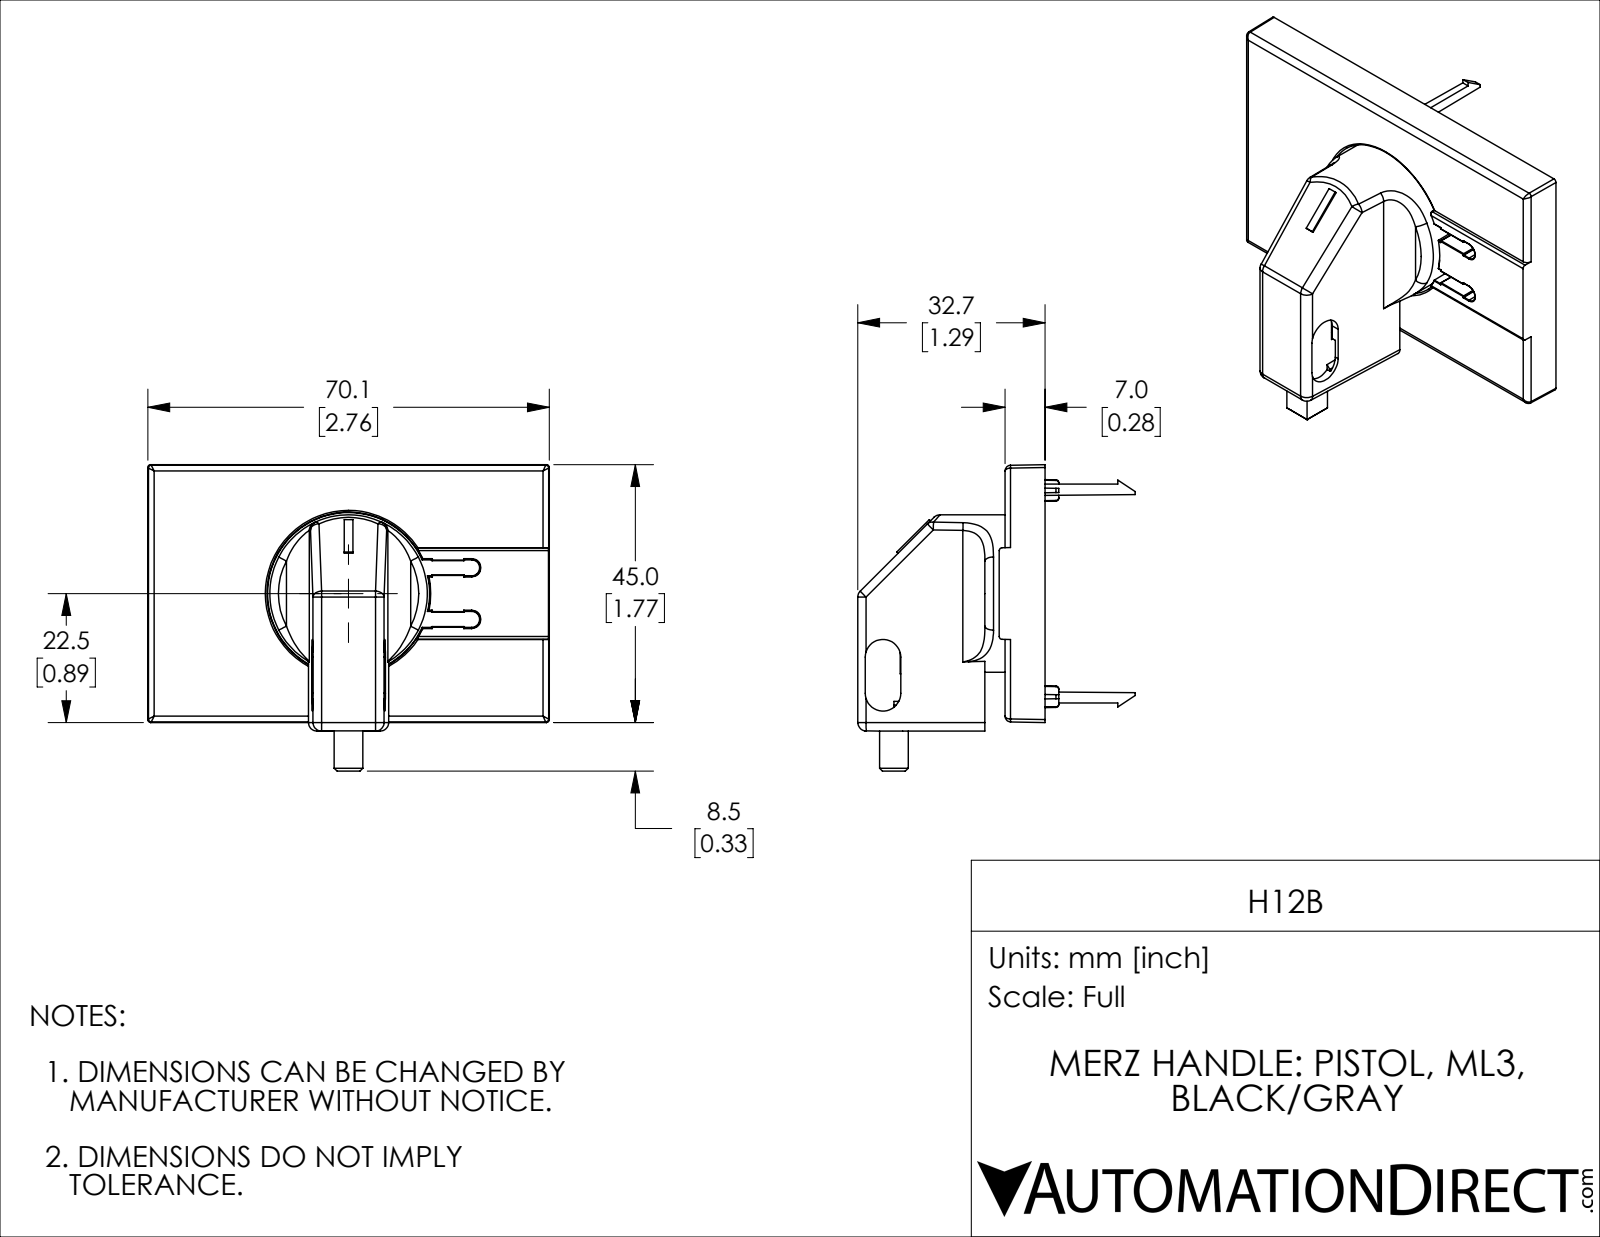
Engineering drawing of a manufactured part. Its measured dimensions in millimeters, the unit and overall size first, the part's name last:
Units: millimetres
Overall size (bounding box): 70.1 × 53.5 × 48.4
Round bosses / shafts (diameter × count): ⌀27.5 ×1
Partial cylindrical surfaces — rounded edges, fillets, slot ends (radius × count): R0.1 ×18, R0.5 ×8, R1.5 ×8, R0.3 ×5, R1 ×4, R3.1 ×2, R4 ×2
Main face-to-face distances: 1, 2, 5, 6, 4, 3, 7, 23.5, 22.9, 21.9
Volume: 17 960 mm³ · Surface area: 18 620 mm²
Bodies: 2 solids, 386 faces (212 planar, 67 cylindrical, 107 other)
Part name (STEP PRODUCT): H12B
STEP written by: SolidWorks 2019 (AUTOMOTIVE_DESIGN)
